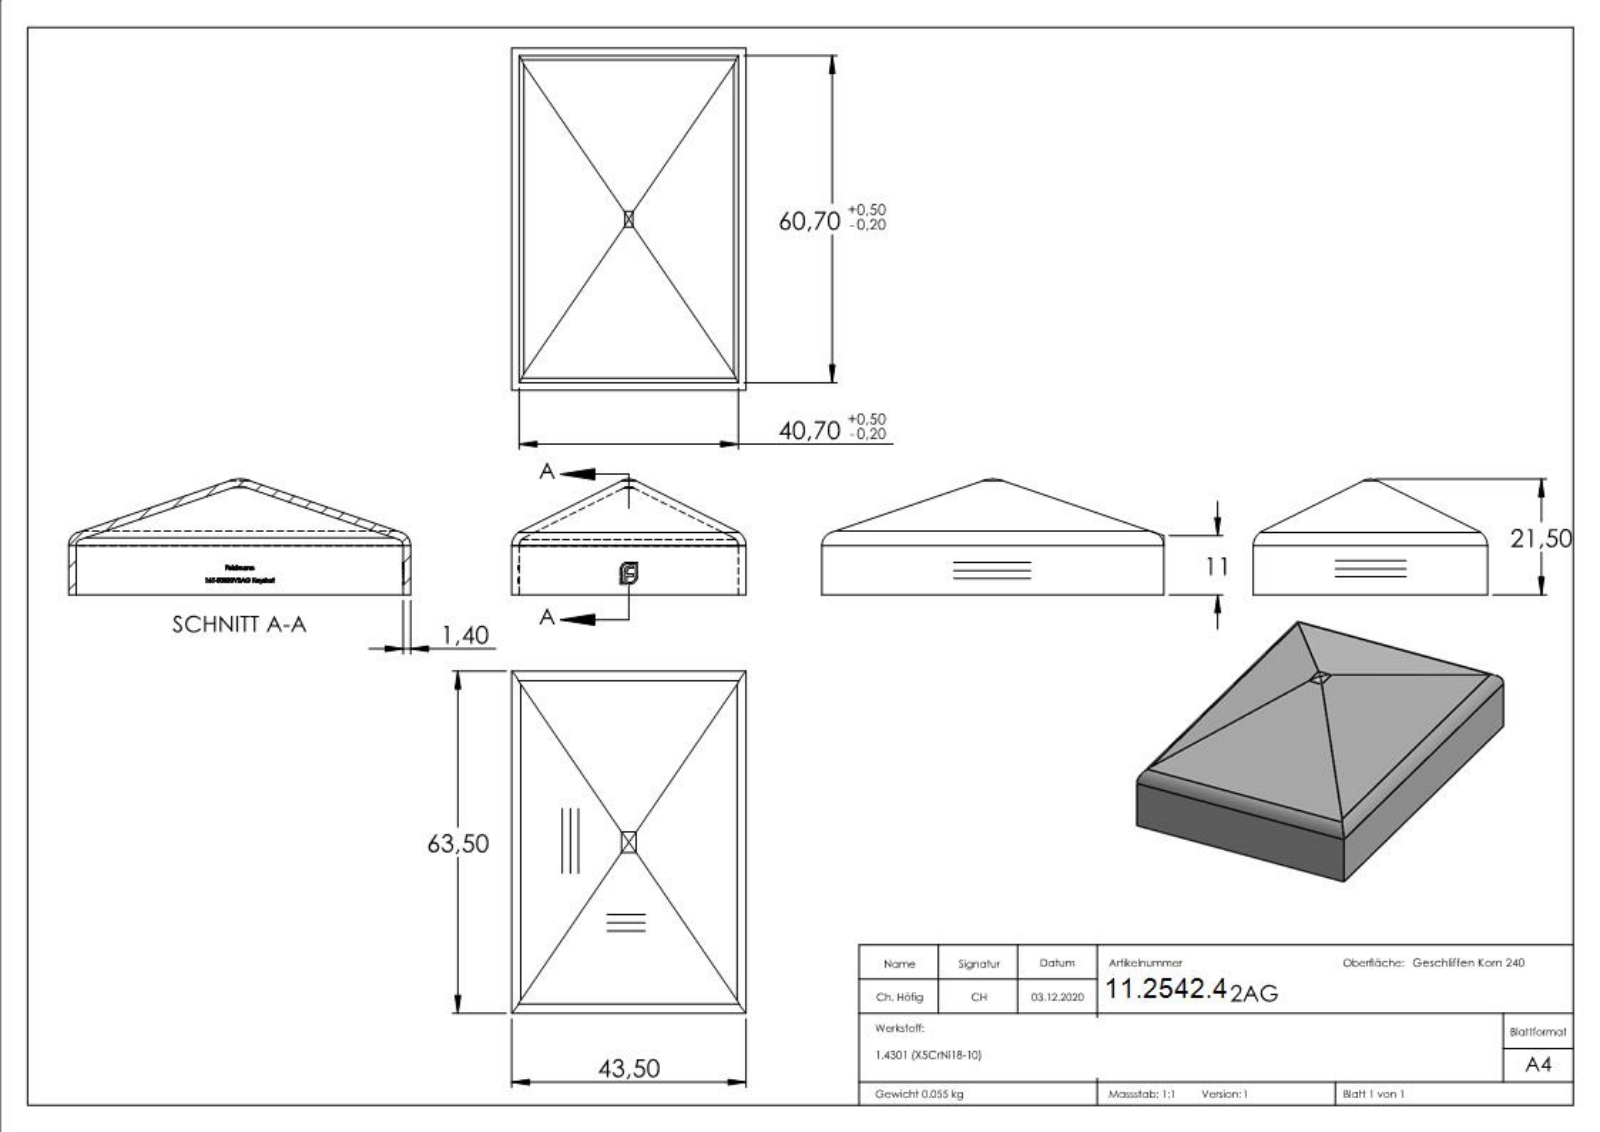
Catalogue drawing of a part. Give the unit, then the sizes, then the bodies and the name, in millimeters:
Units: millimetres
Overall size (bounding box): 63.5 × 43.5 × 21.5
Partial cylindrical surfaces — rounded edges, fillets, slot ends (radius × count): R1.6 ×3, R3 ×3, R1.19 ×2, R2.59 ×2, R4.49 ×1, R5.89 ×1
Main face-to-face distances: 1.4, 42.1, 62.1, 43.5, 40.7, 63.5, 60.7, 1.3, 60.8, 62.2
Volume: 6 958 mm³ · Surface area: 10 249 mm²
Bodies: 1 solid, 340 faces (197 planar, 16 cylindrical, 127 other)
Part name (STEP PRODUCT): 165-60X40V2AG
STEP written by: SolidWorks 2018 (CONFIG_CONTROL_DESIGN)
